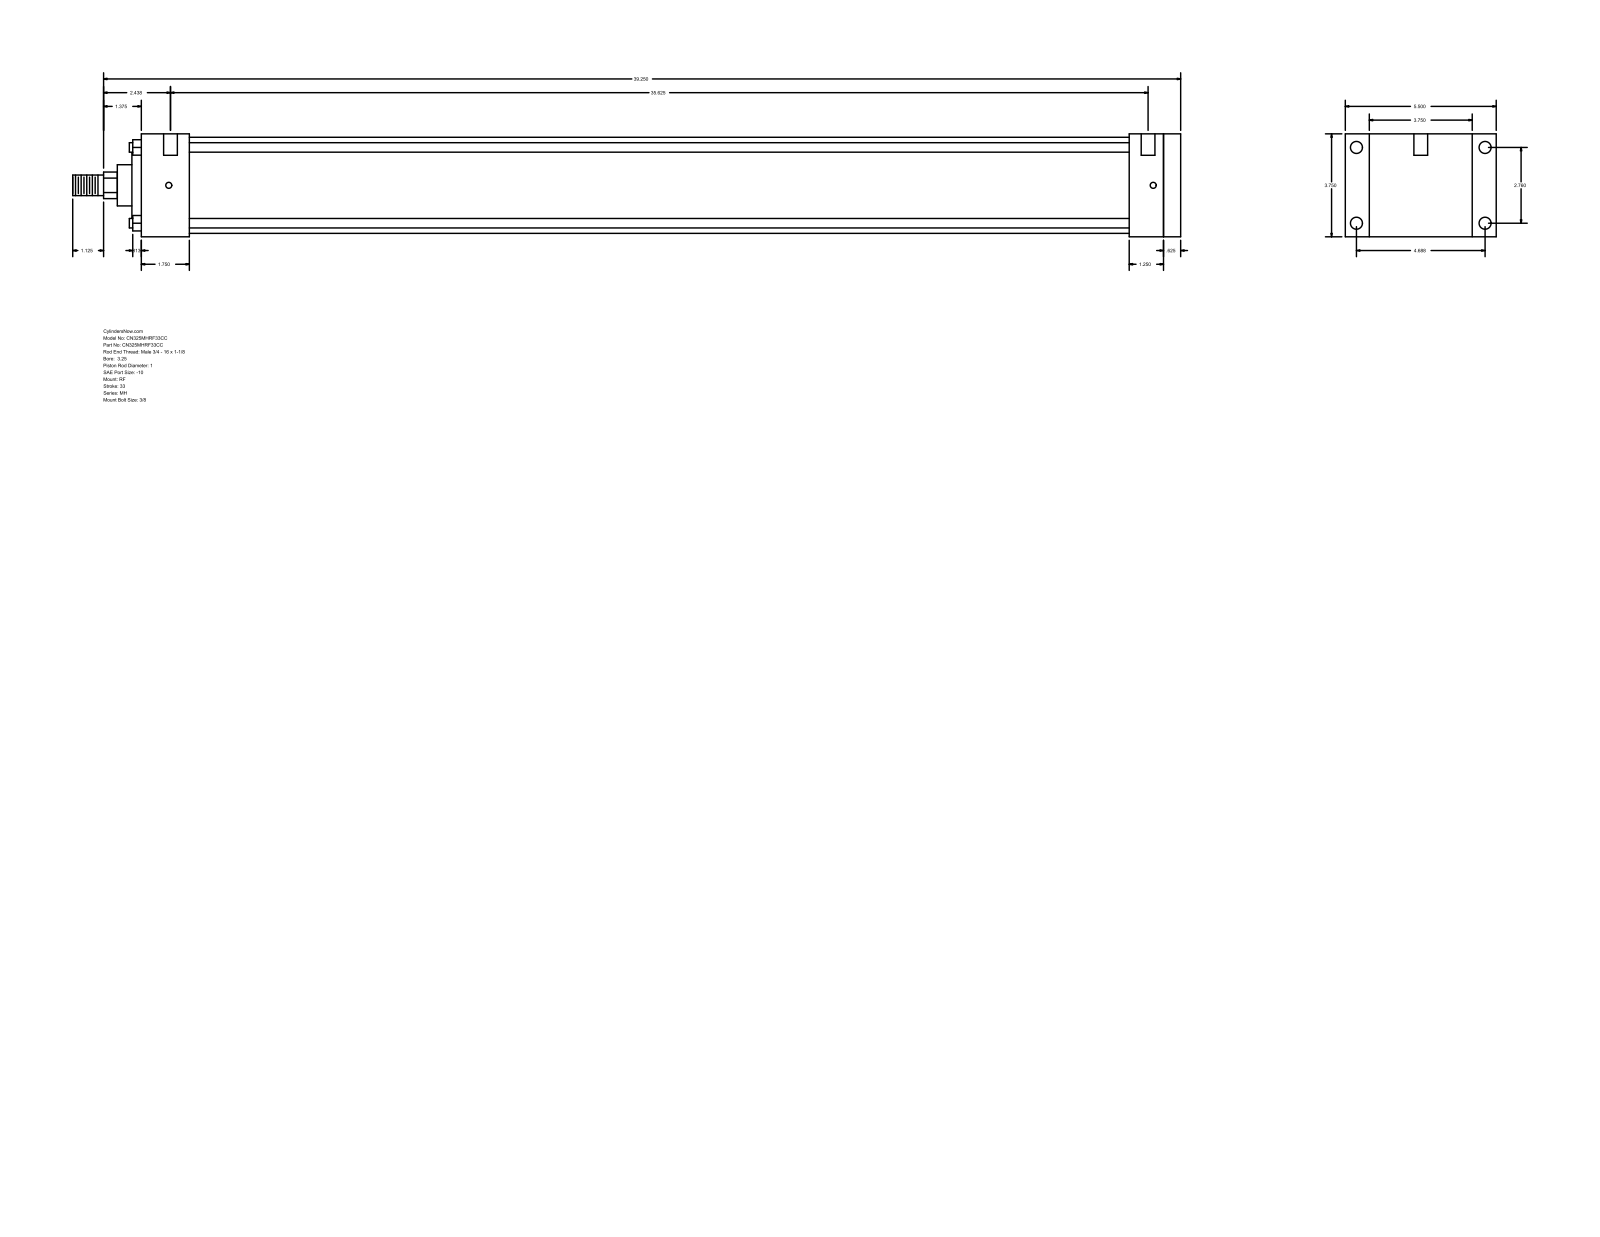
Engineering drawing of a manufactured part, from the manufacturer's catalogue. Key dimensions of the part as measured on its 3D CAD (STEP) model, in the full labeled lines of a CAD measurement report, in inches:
Part name (STEP PRODUCT): MH_RF__0325_1
STEP written by: GSSL Pune (CONFIG_CONTROL_DESIGN)
Units: inches
Bodies: 0 solids, 94 faces (65 planar, 29 cylindrical, 0 other)
Overall size (bounding box): 40.375 × 5.5 × 3.75
Round holes (diameter × count): ⌀0.219 ×4, ⌀0.438 ×4, ⌀0.5 ×2
Round bosses / shafts (diameter × count): ⌀0.345 ×4, ⌀3.5 ×1, ⌀2.375 ×1, ⌀1.5 ×1, ⌀1 ×1, ⌀0.75 ×1
Partial cylindrical surfaces — rounded edges, fillets, slot ends (radius × count): R0.484 ×1
Main face-to-face distances: 3.75, 37.875, 37.25, 0.625, 0.875, 4.625, 1.75, 35.5, 36.125, 36
Hole centre spacings: 2.76, 4.687, 5.439, 35.875, 0.062, 0.187, 35.625, 35.687
